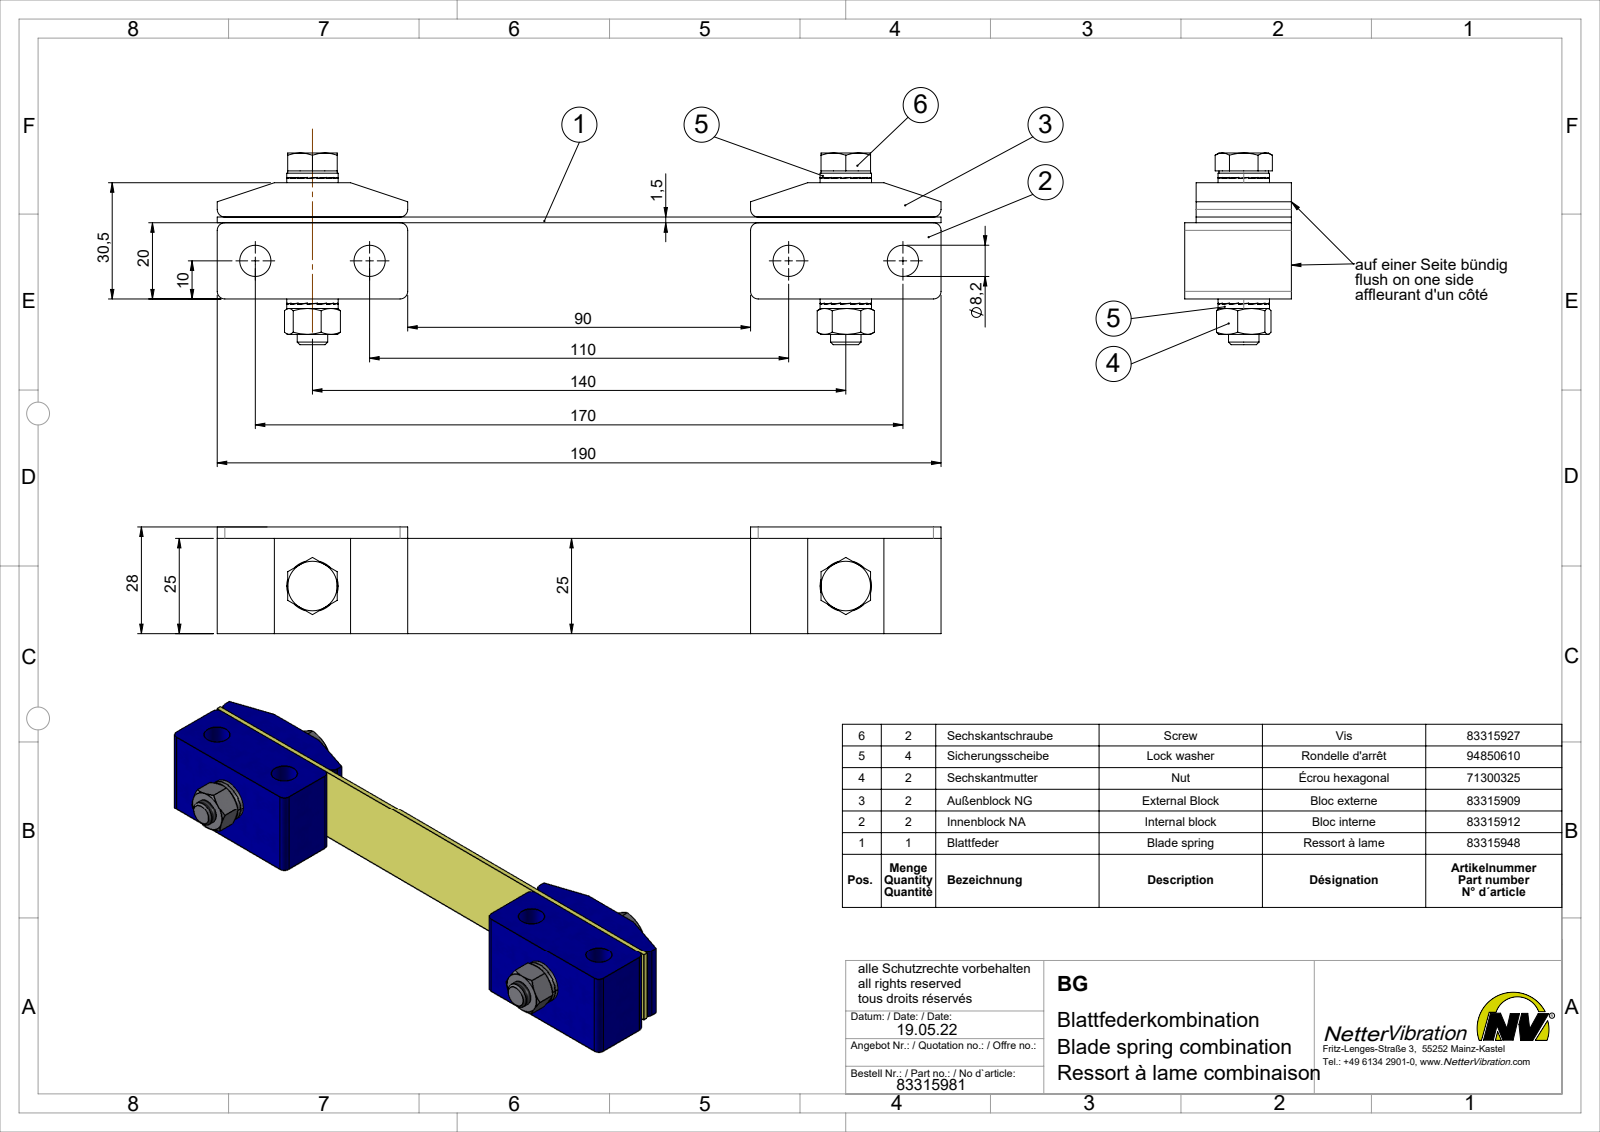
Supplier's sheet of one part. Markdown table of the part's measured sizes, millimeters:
| quantity | value |
| --- | --- |
| part name | Blattfederkombination BG # 83315981 |
| STEP written by | SolidWorks 2015 (AUTOMOTIVE_DESIGN) |
| units | millimeters |
| bodies | 13 solids, 660 faces (536 planar, 72 cylindrical, 52 other) |
| overall size | 190 × 50.3 × 28 |
| volume | 80 799 mm³ |
| surface area | 38 166 mm² |
| round holes (diameter × count) | 8.2 × 6, 6.8 × 2, 8 × 2, 8.5 × 2, 8.7 × 2 |
| round bosses / shafts (diameter × count) | 13.5 × 2, 13 × 2 |
| partial cylindrical surfaces (radius × count) | 2 × 12 |
| main face-to-face distances | 1.5, 21.5, 20, 28, 140, 9, 10.5, 30.5, 3, 25 |
| hole center spacings | 140, 30, 110, 170 |
